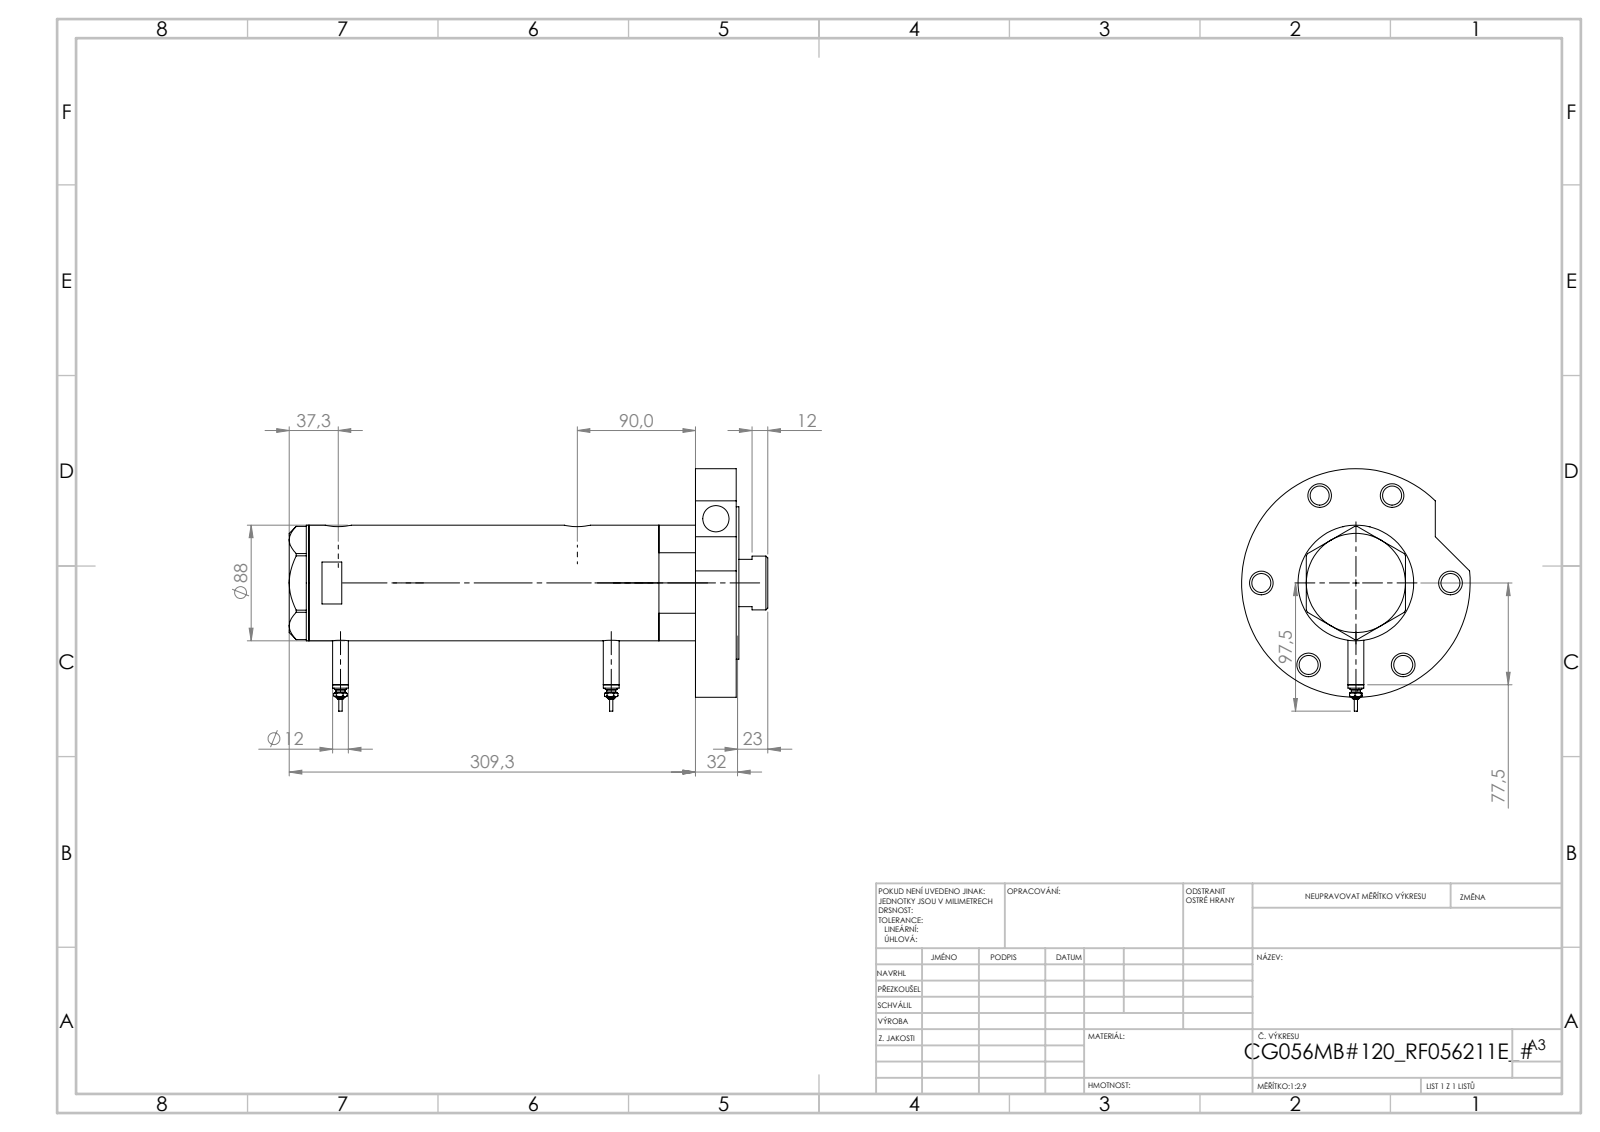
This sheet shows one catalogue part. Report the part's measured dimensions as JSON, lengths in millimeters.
{"part_name": "V270CG_RF211E; V270CG_VC; V270CG_FRONT; V270CG_MIDDLE (+2 more)", "step_written_by": "SolidWorks 2019 (CONFIG_CONTROL_DESIGN)", "units": "millimeters", "bodies": {"solids": 7, "faces": 257, "planar": 91, "cylindrical": 102, "other": 64}, "overall_size": [364.3, 184.5, 174], "volume_mm3": 2411000, "surface_area_mm2": 343161, "round_holes": [[14.5, 7], [18, 6], [20, 3], [12.5, 2], [13.16, 2], [42, 1], [43.5, 1], [56, 1], [60, 1], [75, 1], [80, 1]], "round_bosses_or_shafts": [[12, 2], [9, 2], [7, 2], [4.5, 2], [2.5, 2], [174, 1], [116, 1], [88, 1]], "face_to_face_distances": [31, 2, 327.3, 294.3, 325.3, 33, 204.4, 89.9, 120.9, 122.9], "hole_center_spacings": [72, 80, 119.73, 124.71, 129.15, 143.69, 1.7, 25.8]}
